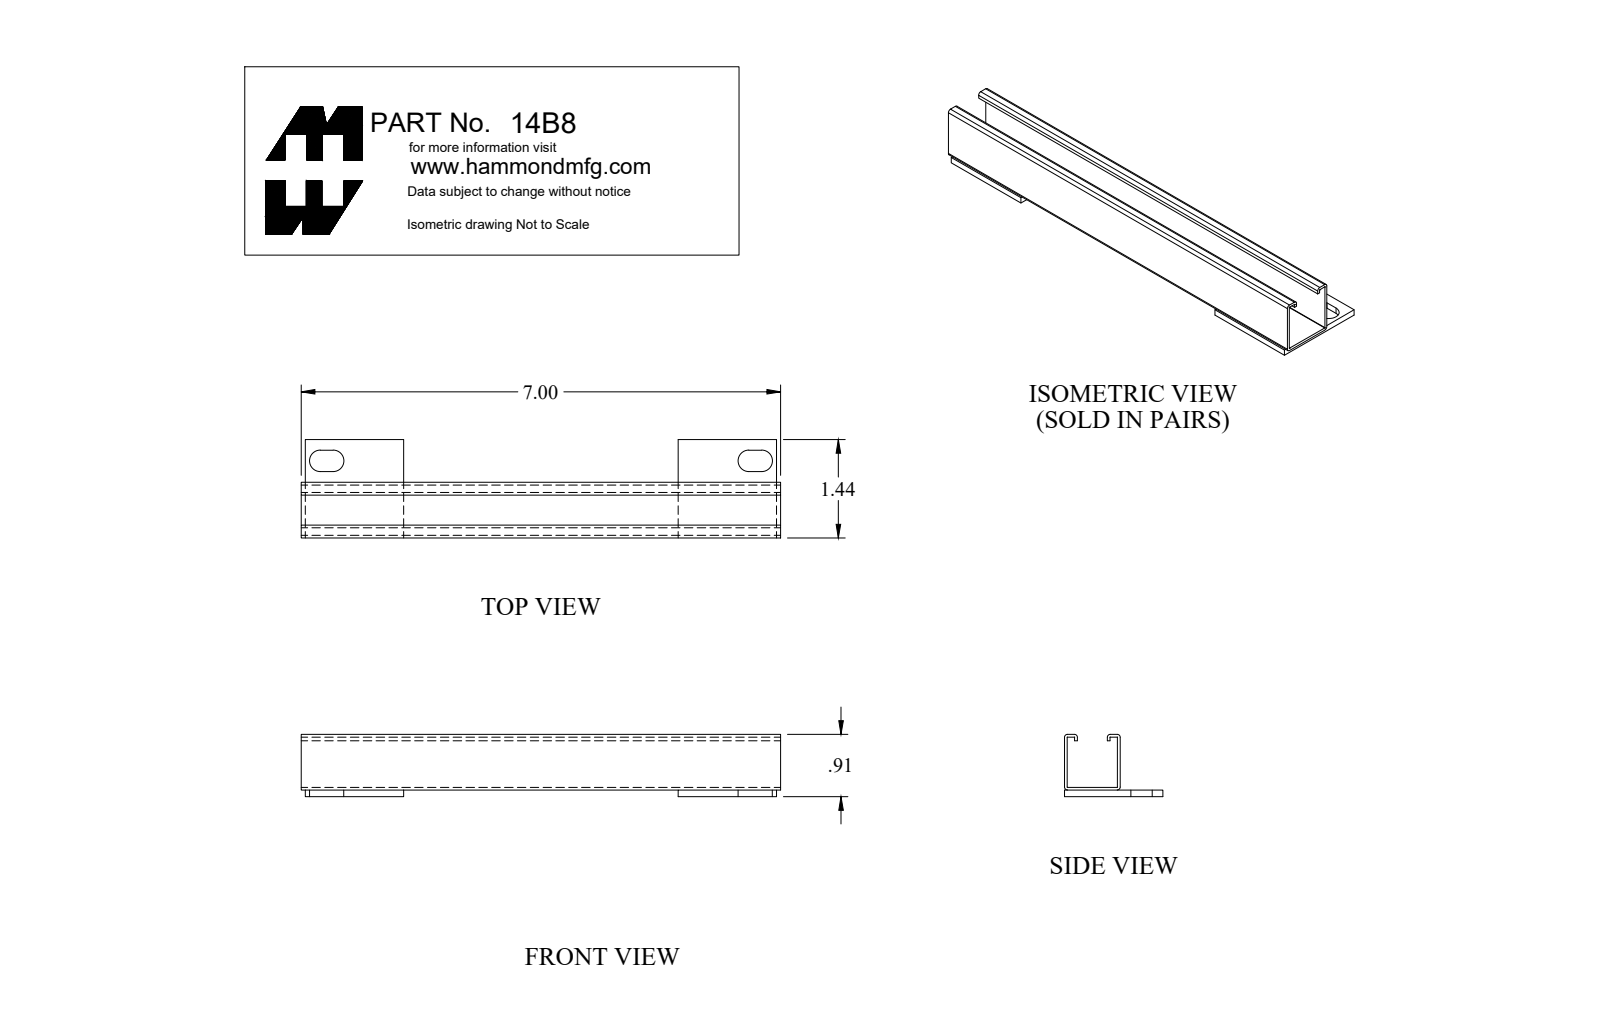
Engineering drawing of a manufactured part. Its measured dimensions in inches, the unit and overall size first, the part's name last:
Units: inches
Overall size (bounding box): 7 × 1.437 × 0.908
Partial cylindrical surfaces — rounded edges, fillets, slot ends (radius × count): R0.043 ×6, R0.156 ×4
Main face-to-face distances: 0.04, 0.773, 0.813, 0.733, 0.095, 0.135, 0.773, 0.868, 0.908, 0.813
Volume: 1.124 in³ · Surface area: 47.7 in²
Bodies: 3 solids, 50 faces (34 planar, 16 cylindrical, 0 other)
Part name (STEP PRODUCT): 14B8
STEP written by: SolidWorks 2018 (AUTOMOTIVE_DESIGN)
